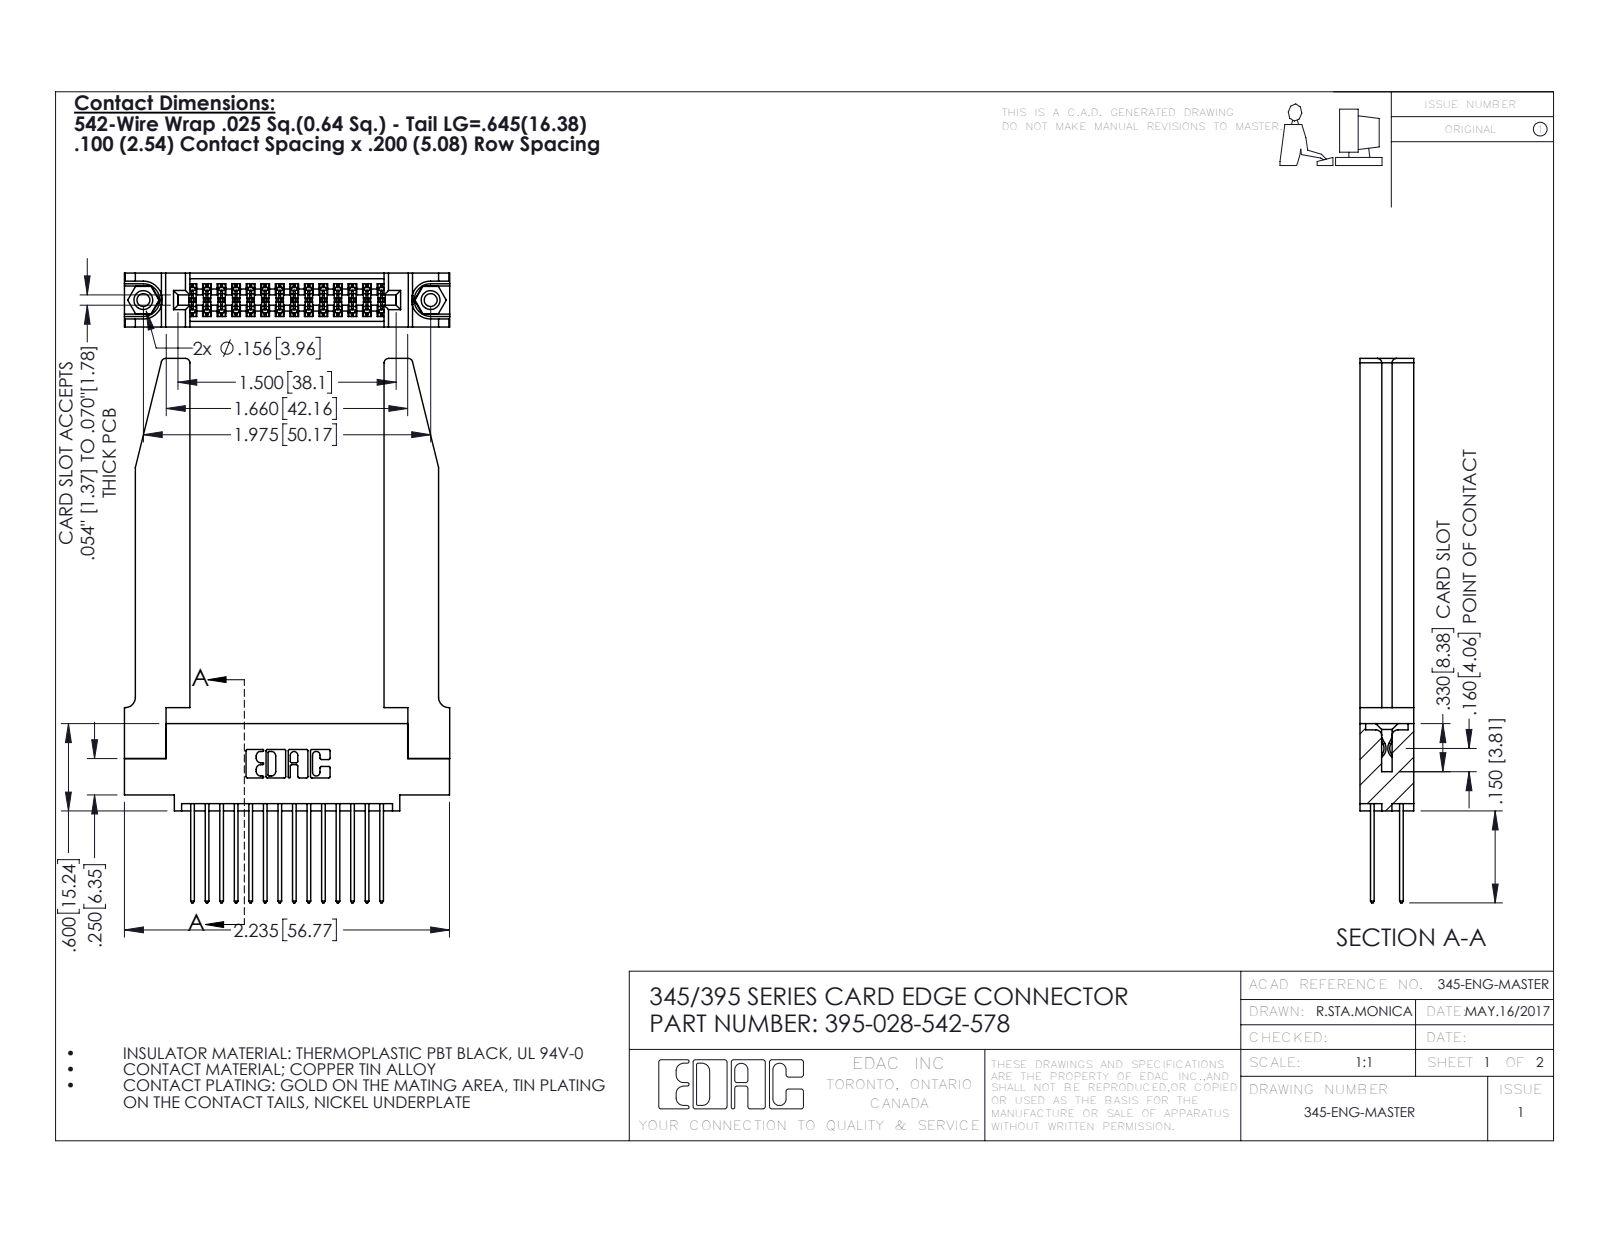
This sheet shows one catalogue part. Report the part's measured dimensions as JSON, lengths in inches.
{"part_name": "345-292-001_345-293-142; 345-220-078_345-220-078; 395-028-542-578; 345 Part_0.110 Offset - 0.156 Dia-TH (+1 more)", "step_written_by": "SolidWorks 2016 (CONFIG_CONTROL_DESIGN)", "units": "inches", "bodies": {"solids": 33, "faces": 1764, "planar": 1150, "cylindrical": 562, "other": 52}, "overall_size": [3.742, 2.236, 0.37], "volume_in3": 0.798, "surface_area_in2": 23.02, "round_holes": [[0.089, 2], [0.125, 2], [0.156, 2], [0.064, 1]], "round_bosses_or_shafts": [[0.155, 2]], "partial_cylinders_radius": [[0.006, 42], [0.01, 28], [0.01, 22], [0.03, 8], [0.007, 6], [0.031, 6], [0.026, 3], [0.014, 2]], "face_to_face_distances": [0.37, 0.072, 0.298, 0.2, 0.098, 0.272, 0.025, 0.148, 0.15, 0.225], "hole_center_spacings": [0.27, 1.742, 1.975]}
